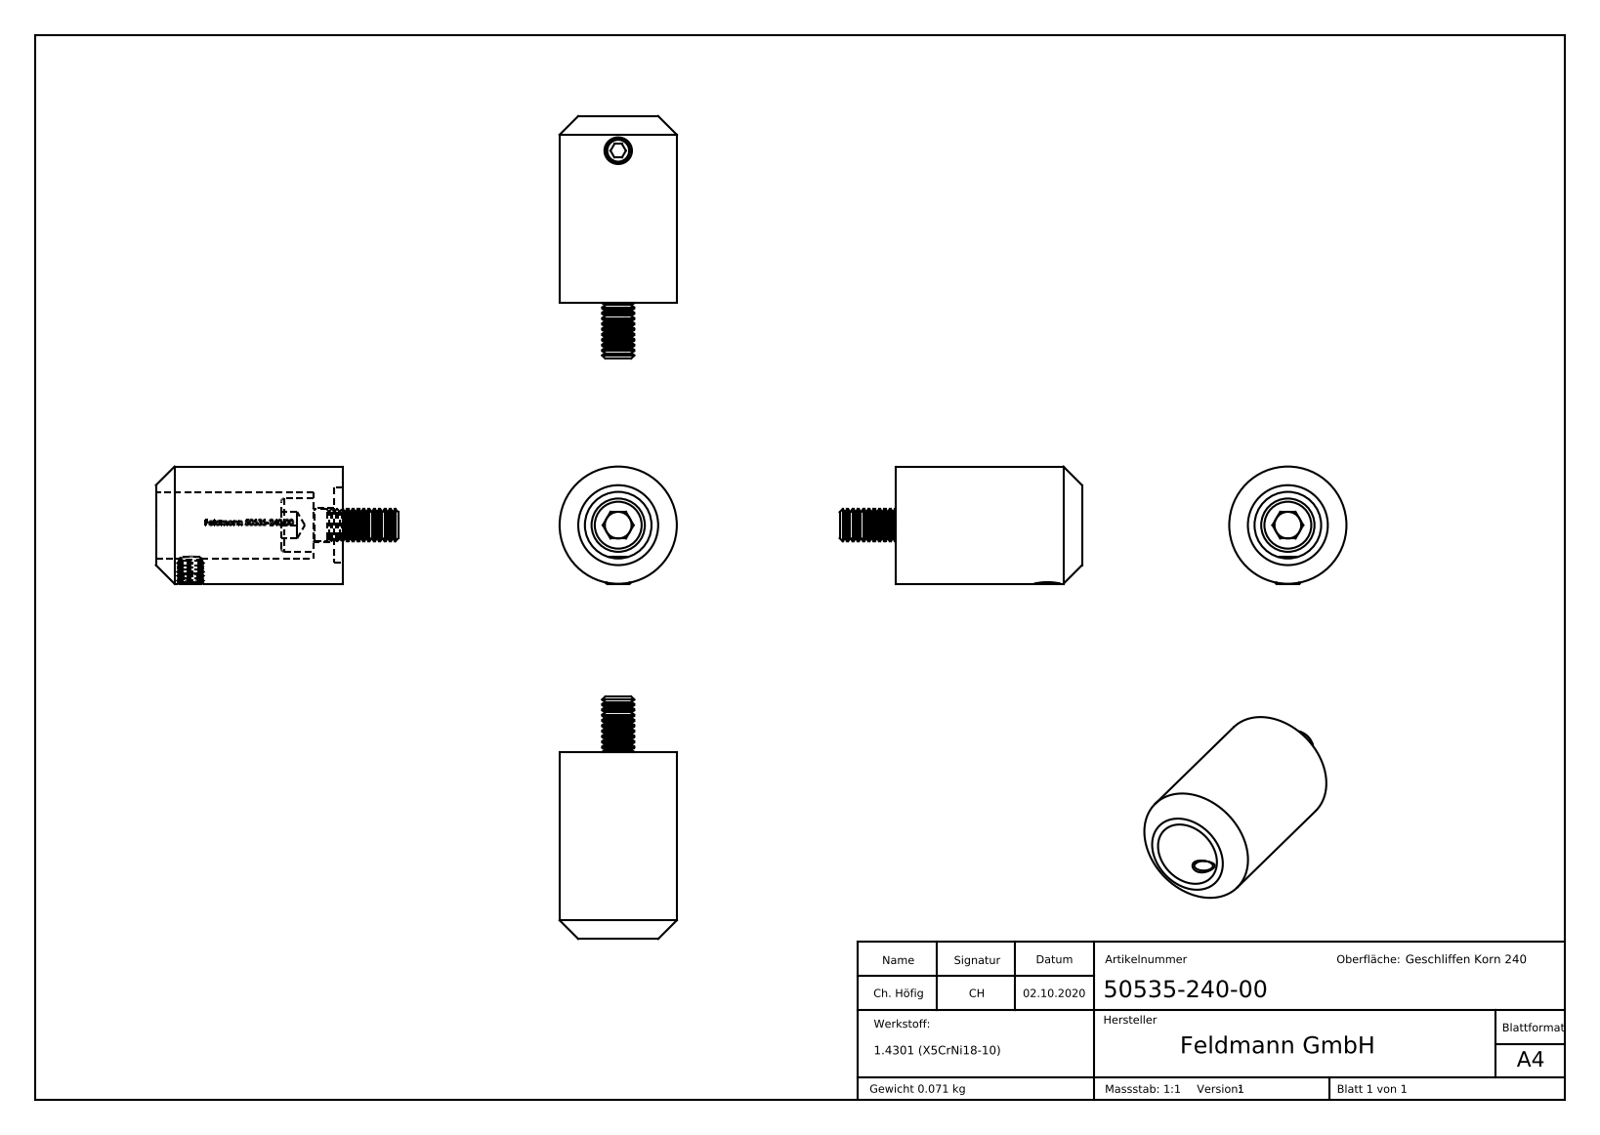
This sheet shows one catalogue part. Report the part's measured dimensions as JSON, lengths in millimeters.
{"part_name": "socket head cap screw_din; socket set screw flat point_din; 50535-240-00; socket head cap screw_din_DIN 912 M6 x 16 --- 16S (+3 more)", "step_written_by": "SolidWorks 2018 (CONFIG_CONTROL_DESIGN)", "units": "millimeters", "bodies": {"solids": 3, "faces": 434, "planar": 150, "cylindrical": 64, "other": 220}, "overall_size": [45.5, 22, 22], "volume_mm3": 9740, "surface_area_mm2": 5254, "round_holes": [[4.2, 1], [6.5, 1], [12.5, 1], [14, 1]], "round_bosses_or_shafts": [[22, 1], [10, 1], [6, 1], [5, 1]], "face_to_face_distances": [5.5, 1.5, 4, 35, 33.5, 29.5, 6, 11.5, 10, 23.5]}
